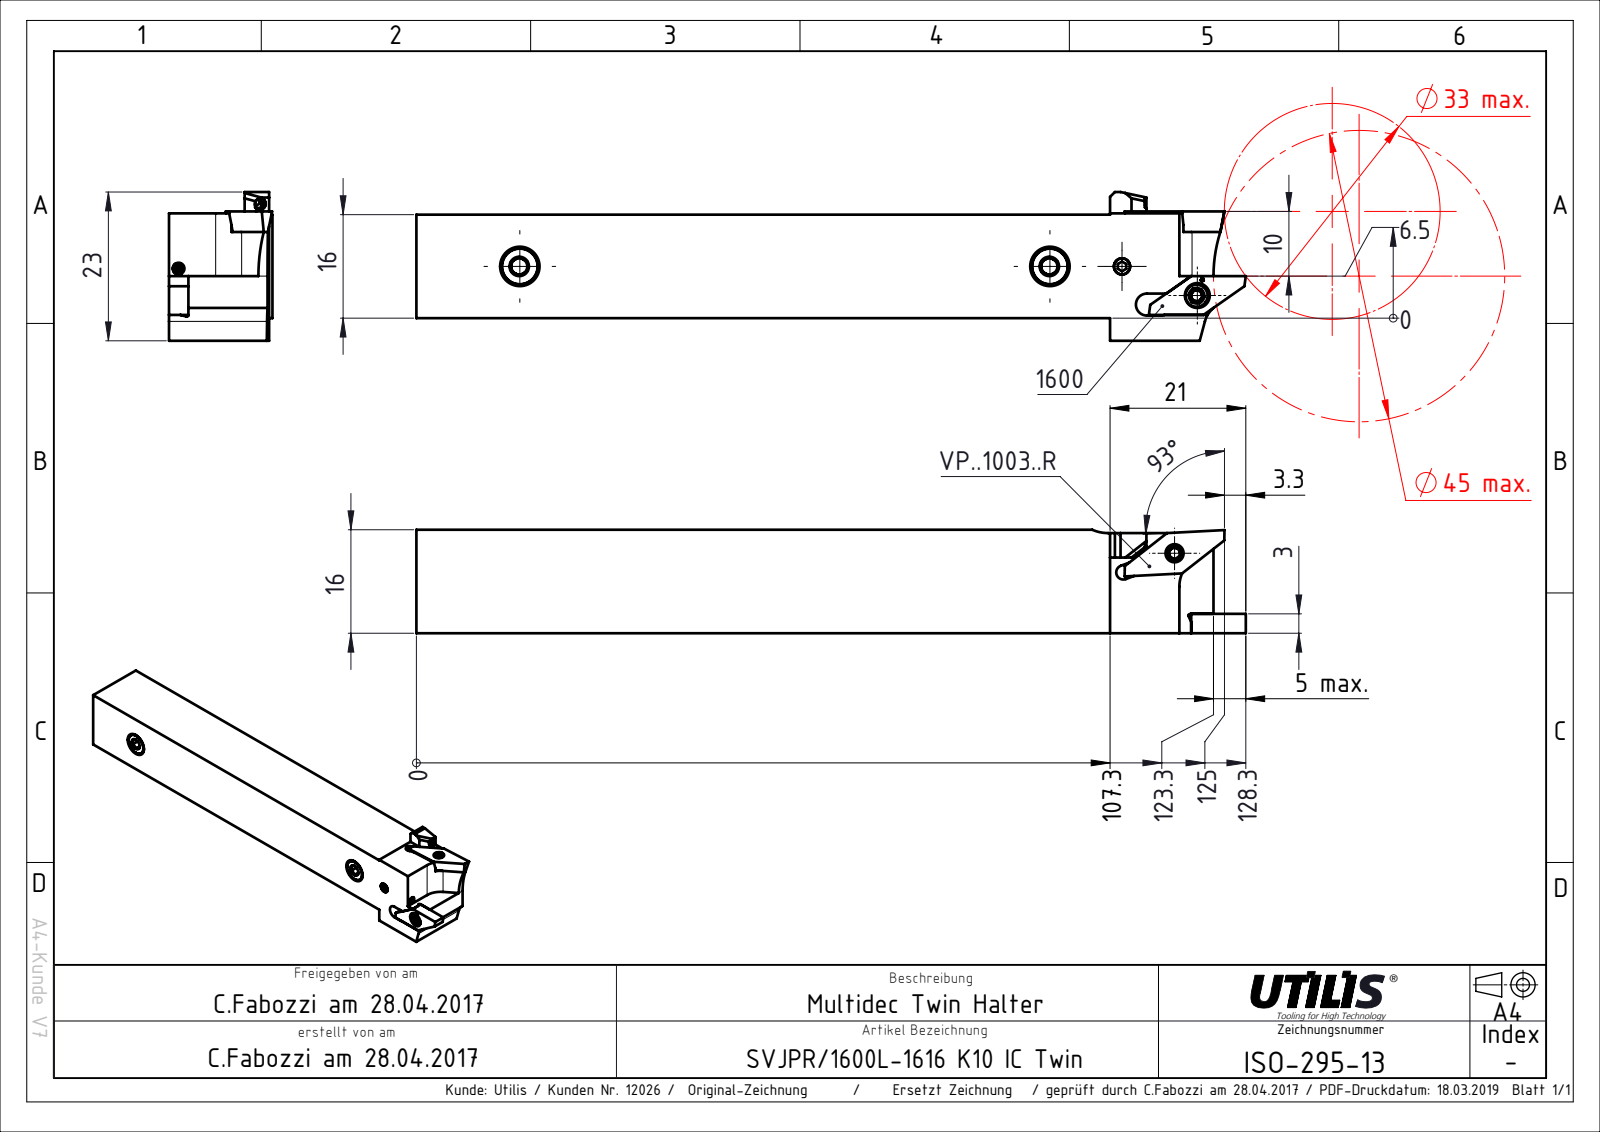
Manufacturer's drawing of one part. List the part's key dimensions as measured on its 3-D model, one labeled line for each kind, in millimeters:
Part name (STEP PRODUCT): ISO-295-13
STEP written by: SolidWorks 2016 (AUTOMOTIVE_DESIGN)
Units: millimetres
Bodies: 1 solid, 81 faces (67 planar, 12 cylindrical, 2 other)
Overall size (bounding box): 128.3 × 23 × 16
Volume: 31 752 mm³ · Surface area: 8 842 mm²
Partial cylindrical surfaces — rounded edges, fillets, slot ends (radius × count): R0.25 ×2, R6.1 ×2, R0.5 ×1, R1.1 ×1, R1.55 ×1, R1.7 ×1, R4.1 ×1, R5.1 ×1
Main face-to-face distances: 16, 3.5, 19.5, 10, 19.7, 16.2, 0.5, 6.5, 9.5, 9.7
